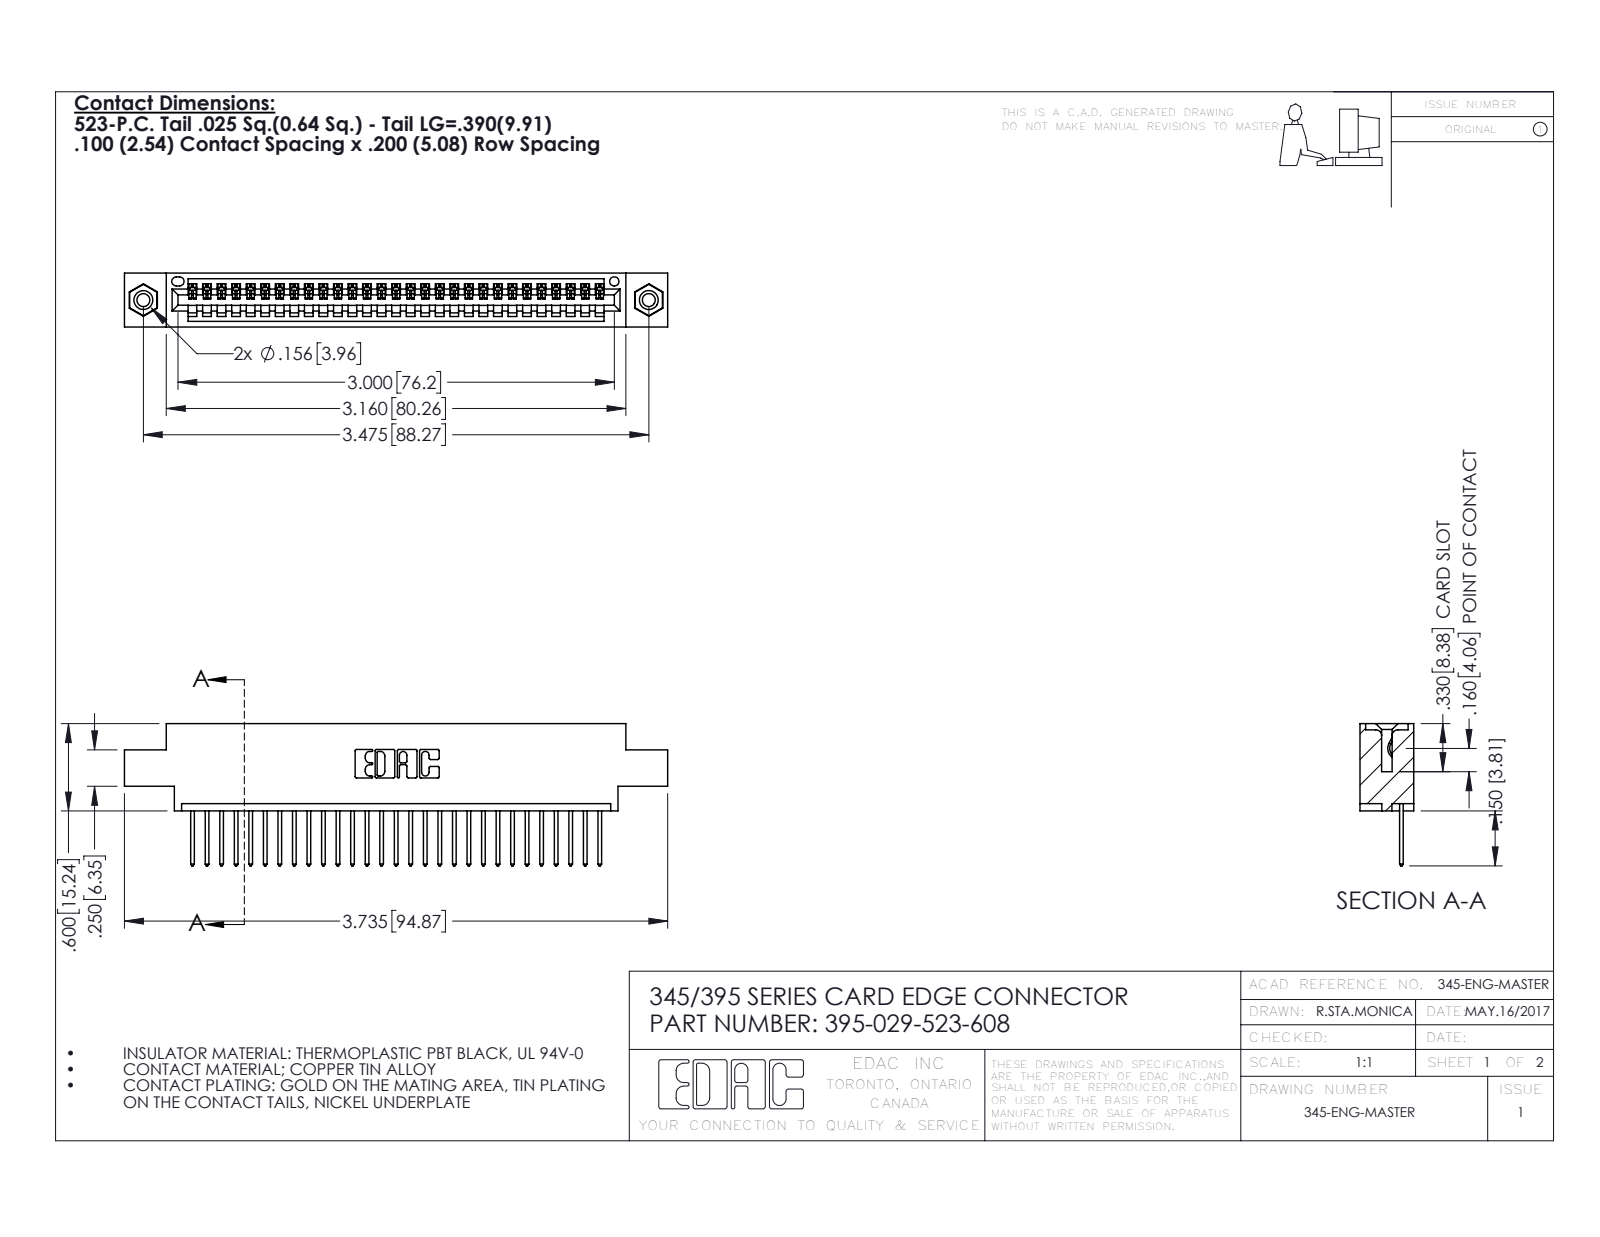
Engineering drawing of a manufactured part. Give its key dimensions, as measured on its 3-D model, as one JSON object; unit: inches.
{"part_name": "345-250-001_345-250-003-102; 345 Part_0.170 Offset - 0.156 Dia-TI; 395-029-523-608; 345-292-001_345-293-123", "step_written_by": "SolidWorks 2016 (CONFIG_CONTROL_DESIGN)", "units": "inches", "bodies": {"solids": 32, "faces": 1872, "planar": 1276, "cylindrical": 580, "other": 16}, "overall_size": [3.735, 0.977, 0.37], "volume_in3": 0.535, "surface_area_in2": 18.07, "round_holes": [[0.089, 2], [0.125, 2], [0.156, 2], [0.064, 1]], "round_bosses_or_shafts": [[0.155, 2]], "partial_cylinders_radius": [[0.006, 58], [0.01, 58], [0.01, 22], [0.007, 6], [0.031, 6], [0.026, 3], [0.031, 2], [0.04, 2]], "face_to_face_distances": [0.072, 0.298, 0.37, 0.2, 0.098, 0.272, 0.025, 0.225, 0.175, 0.149], "hole_center_spacings": [0.27, 3.24, 3.475]}
